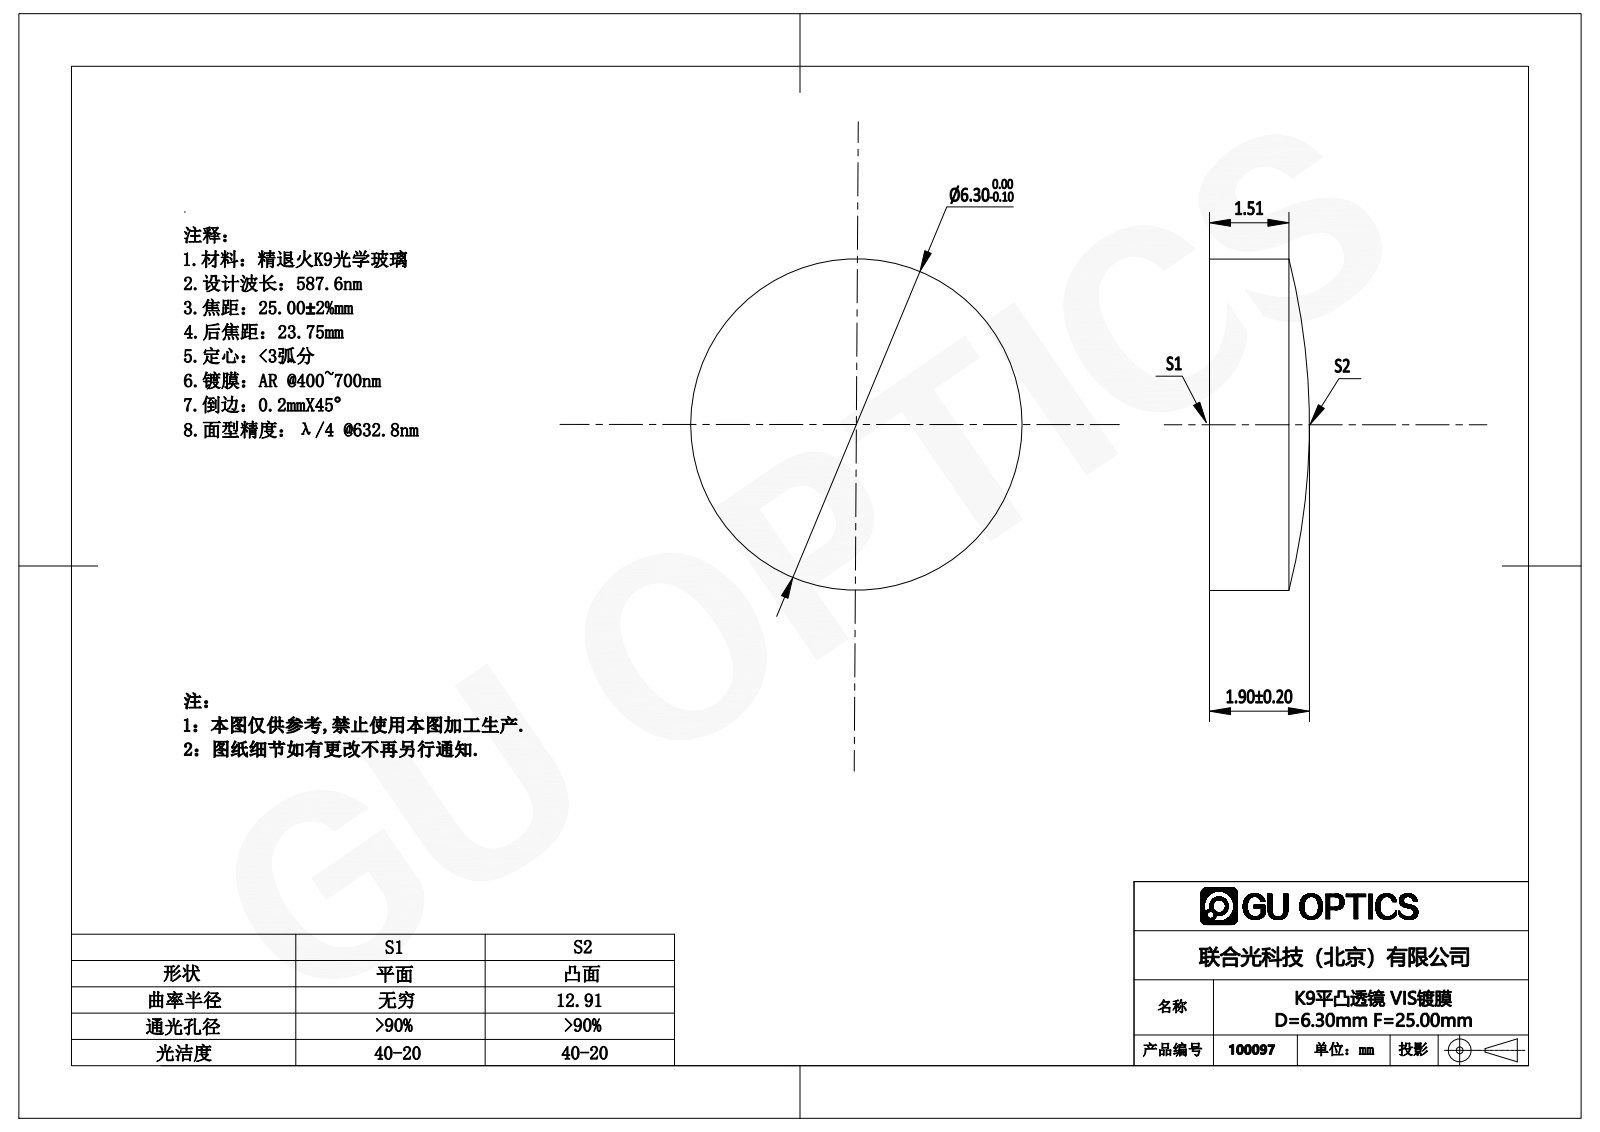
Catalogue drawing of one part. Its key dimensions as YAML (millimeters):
part_name: "100097"
step_written_by: "SolidWorks 2016 (AUTOMOTIVE_DESIGN)"
units: millimeters
bodies: {solids: 1, faces: 5, planar: 1, cylindrical: 2, other: 2}
overall_size: [6.3, 6.3, 1.9]
volume: 53
surface_area: 93
round_bosses_or_shafts:
  - {diameter: 6.3, count: 1}
